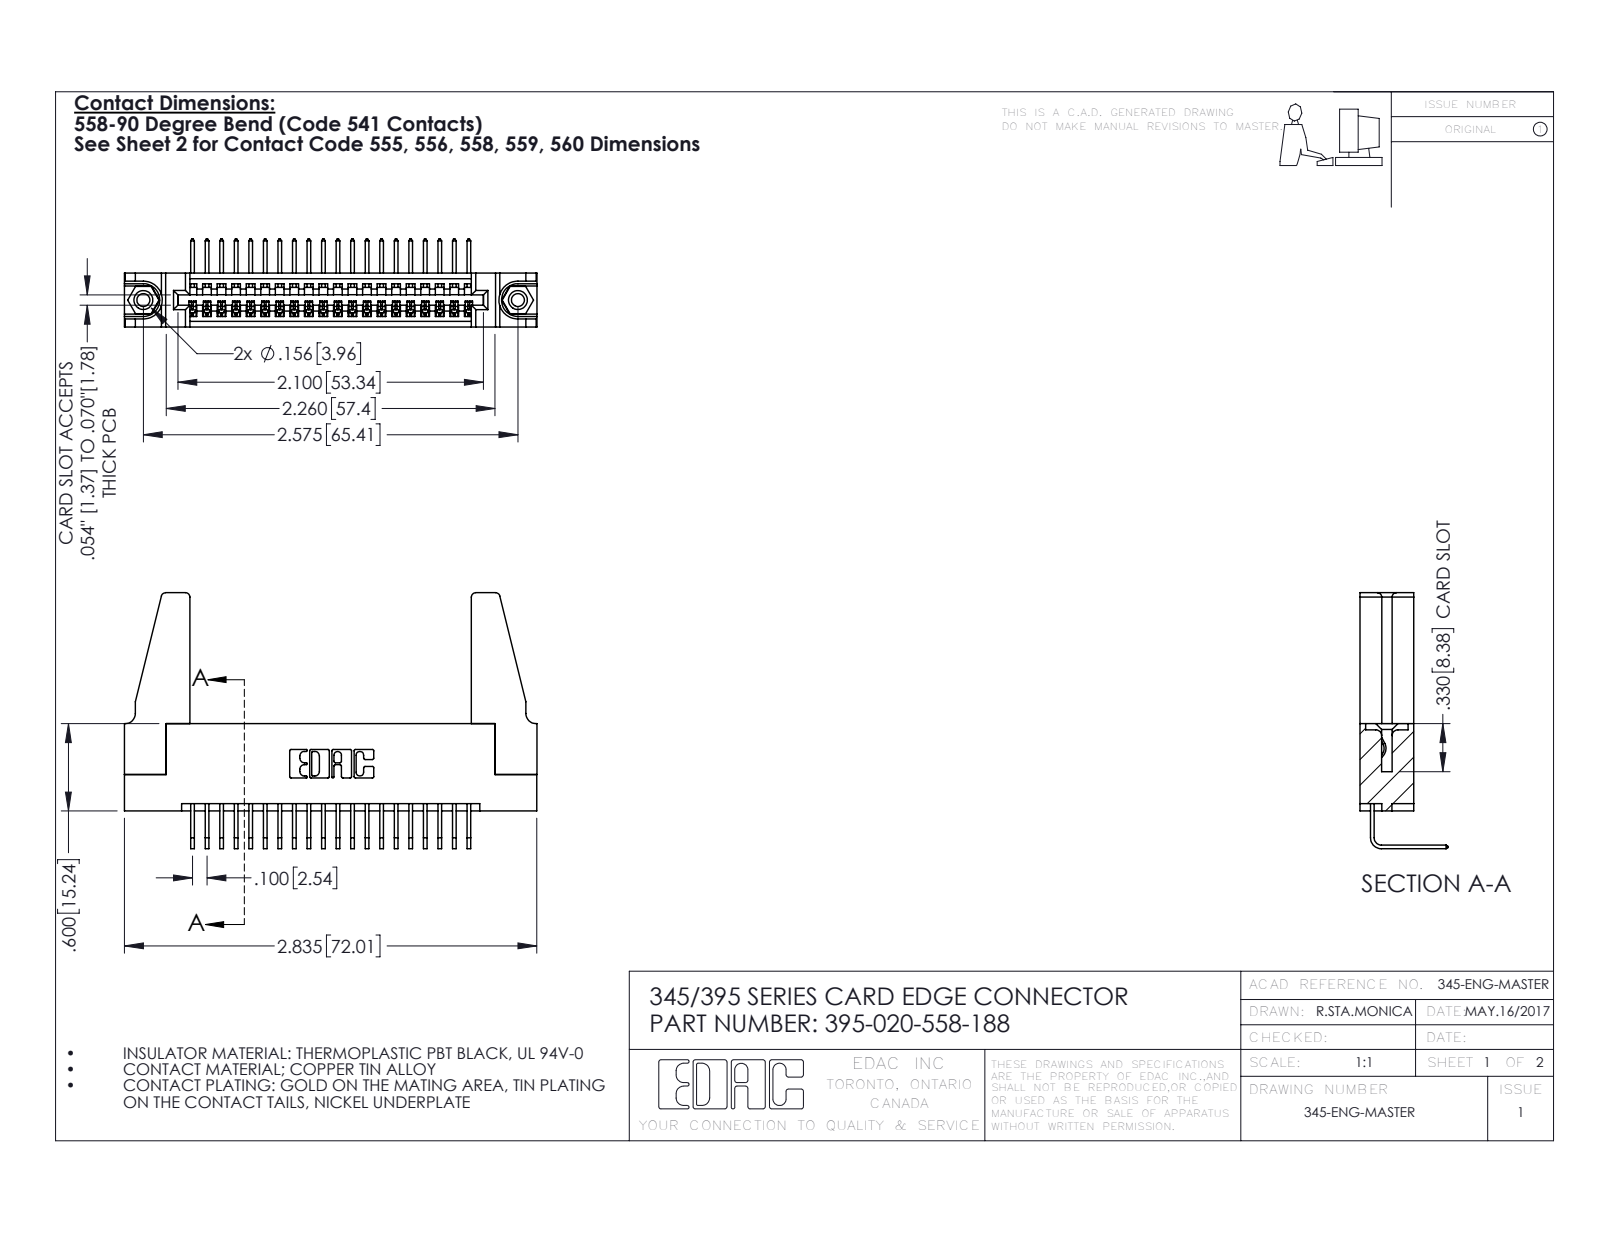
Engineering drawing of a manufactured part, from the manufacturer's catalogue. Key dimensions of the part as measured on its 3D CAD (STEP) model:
Part name (STEP PRODUCT): 345-220-078_345-220-088; 345 Part_Flush Mounting Lugs - 0.156 Dia-TH; 395-020-558-188; 345-250-001_345-250-001-102 (+1 more)
STEP written by: SolidWorks 2016 (CONFIG_CONTROL_DESIGN)
Units: inches
Bodies: 25 solids, 1450 faces (992 planar, 442 cylindrical, 16 other)
Overall size (bounding box): 2.836 × 1.759 × 0.605
Volume: 0.609 in³ · Surface area: 18.85 in²
Round holes (diameter × count): ⌀0.089 ×2, ⌀0.125 ×2, ⌀0.156 ×2, ⌀0.064 ×1
Round bosses / shafts (diameter × count): ⌀0.155 ×2
Partial cylindrical surfaces — rounded edges, fillets, slot ends (radius × count): R0.006 ×40, R0.01 ×22, R0.03 ×8, R0.007 ×6, R0.031 ×6, R0.026 ×3, R0.031 ×2, R0.04 ×2
Main face-to-face distances: 0.37, 0.072, 0.298, 0.2, 0.098, 0.272, 0.025, 0.225, 0.148, 0.15
Hole centre spacings: 0.27, 2.341, 2.575
